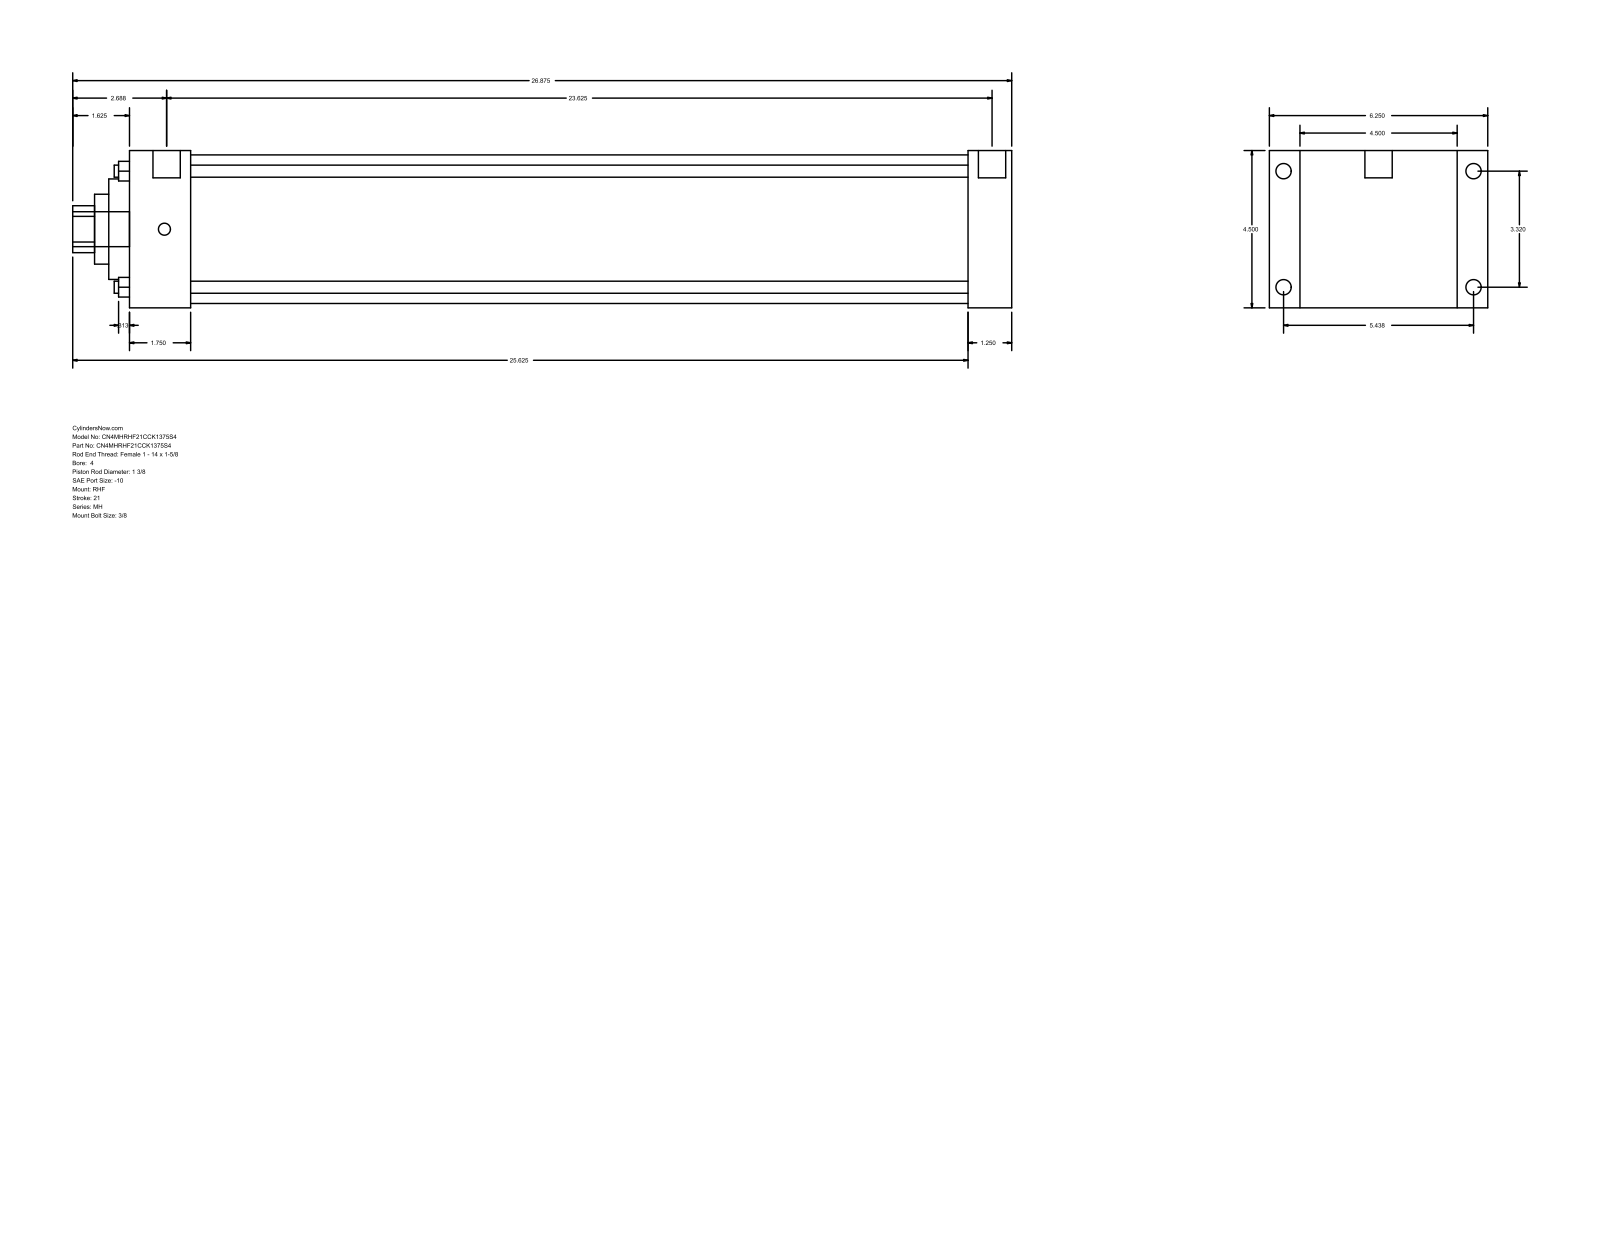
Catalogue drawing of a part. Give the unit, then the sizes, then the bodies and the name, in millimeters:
Units: millimetres
Overall size (bounding box): 682.62 × 158.75 × 114.3
Round holes (diameter × count): ⌀8.76 ×4, ⌀34.92 ×1, ⌀50.8 ×1, ⌀73.03 ×1, ⌀107.95 ×1
Round bosses / shafts (diameter × count): ⌀11.13 ×4, ⌀8.73 ×4, ⌀19.84 ×2, ⌀25.4 ×1
Partial cylindrical surfaces — rounded edges, fillets, slot ends (radius × count): R17.06 ×1
Main face-to-face distances: 114.3, 641.35, 609.61, 31.74, 22.23, 136.53, 44.45, 565.16, 596.9, 158.76
Hole centre spacings: 59.62, 84.32, 119.25
Bodies: 0 solids, 90 faces (61 planar, 29 cylindrical, 0 other)
Part name (STEP PRODUCT): MH_RHF__0400_1.375
STEP written by: GSSL Pune (CONFIG_CONTROL_DESIGN)
